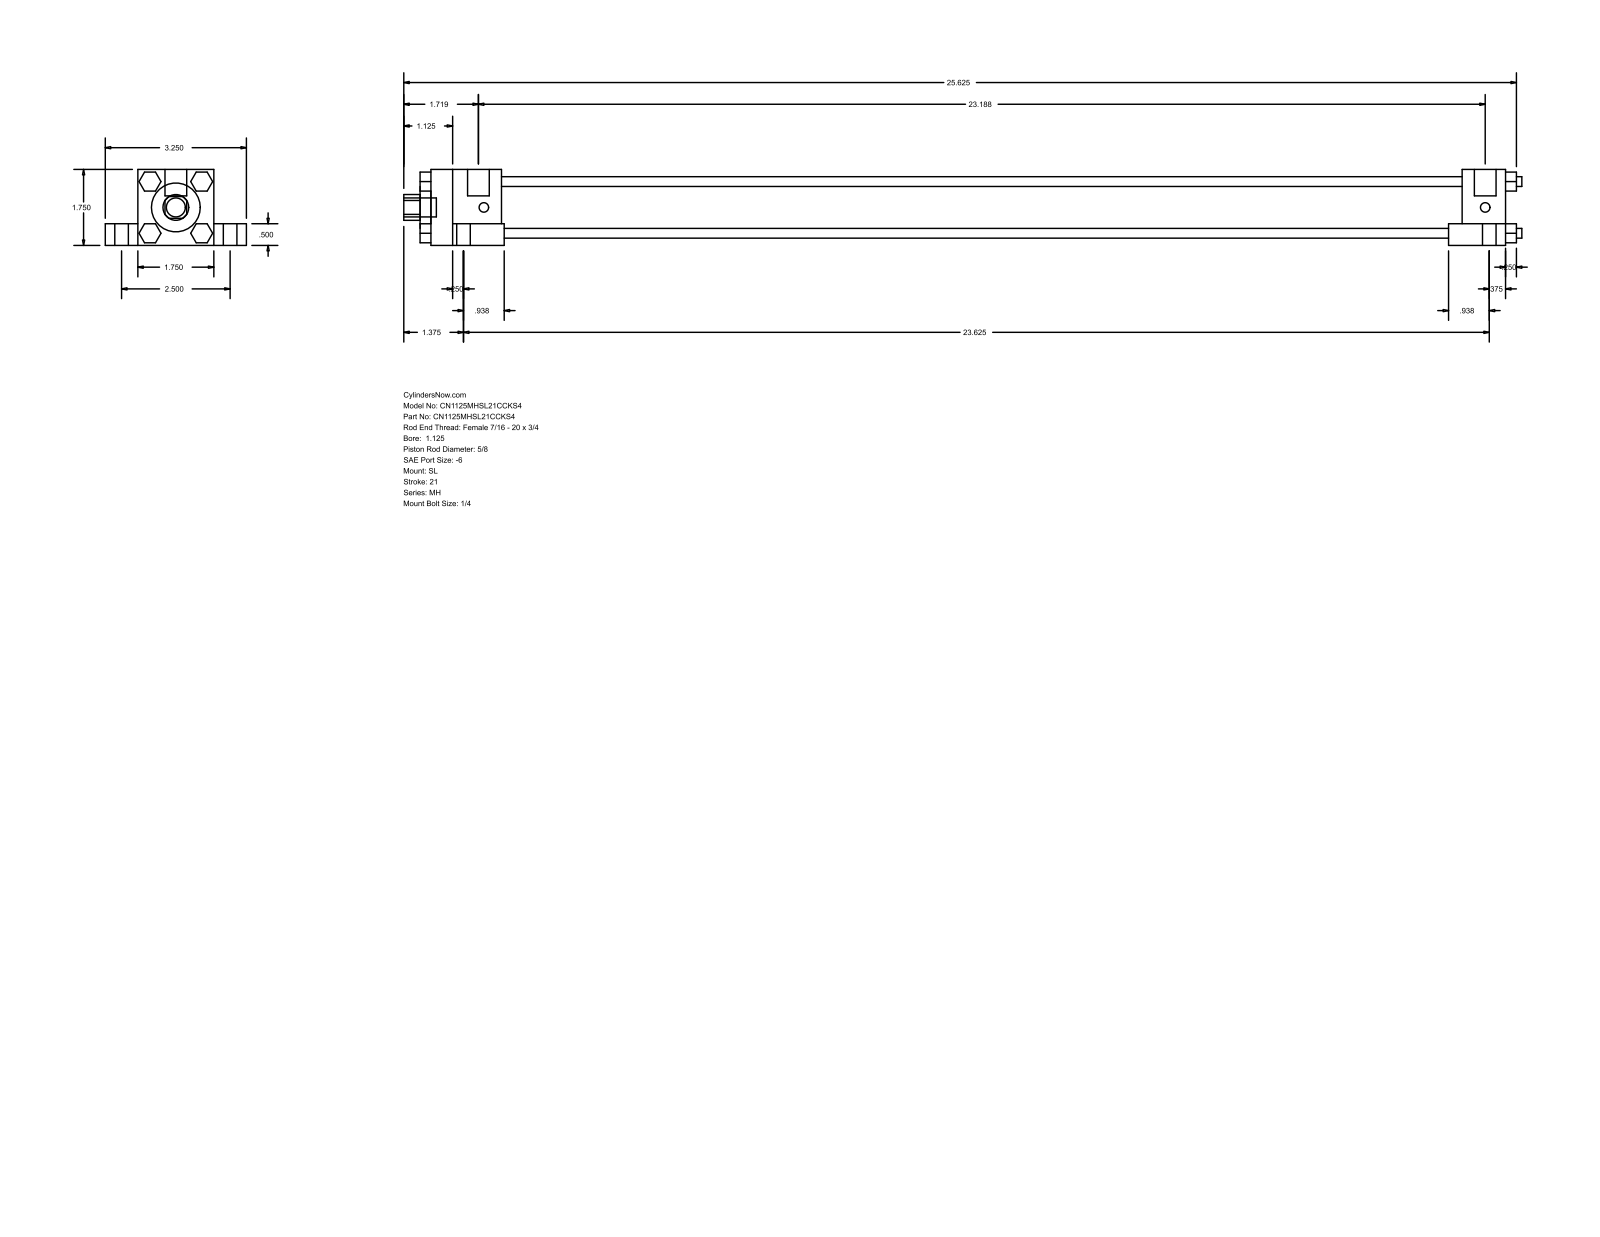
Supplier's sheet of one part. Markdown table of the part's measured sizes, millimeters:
| quantity | value |
| --- | --- |
| part name | MH_SL__0112_0.625 |
| STEP written by | GSSL Pune (CONFIG_CONTROL_DESIGN) |
| units | millimeters |
| bodies | 0 solids, 150 faces (114 planar, 36 cylindrical, 0 other) |
| overall size | 654.05 × 82.55 × 44.45 |
| round holes (diameter × count) | 15.88 × 1, 28.57 × 1, 34.92 × 1 |
| round bosses / shafts (diameter × count) | 14.29 × 4, 7.94 × 4, 5.71 × 4, 5.56 × 4, 12.7 × 2, 11.11 × 1 |
| partial cylindrical surfaces (radius × count) | 7.54 × 1 |
| main face-to-face distances | 44.46, 31.76, 19.04, 12.7, 63.5, 11.11, 561.97, 587.37, 25.4, 41.27 |
